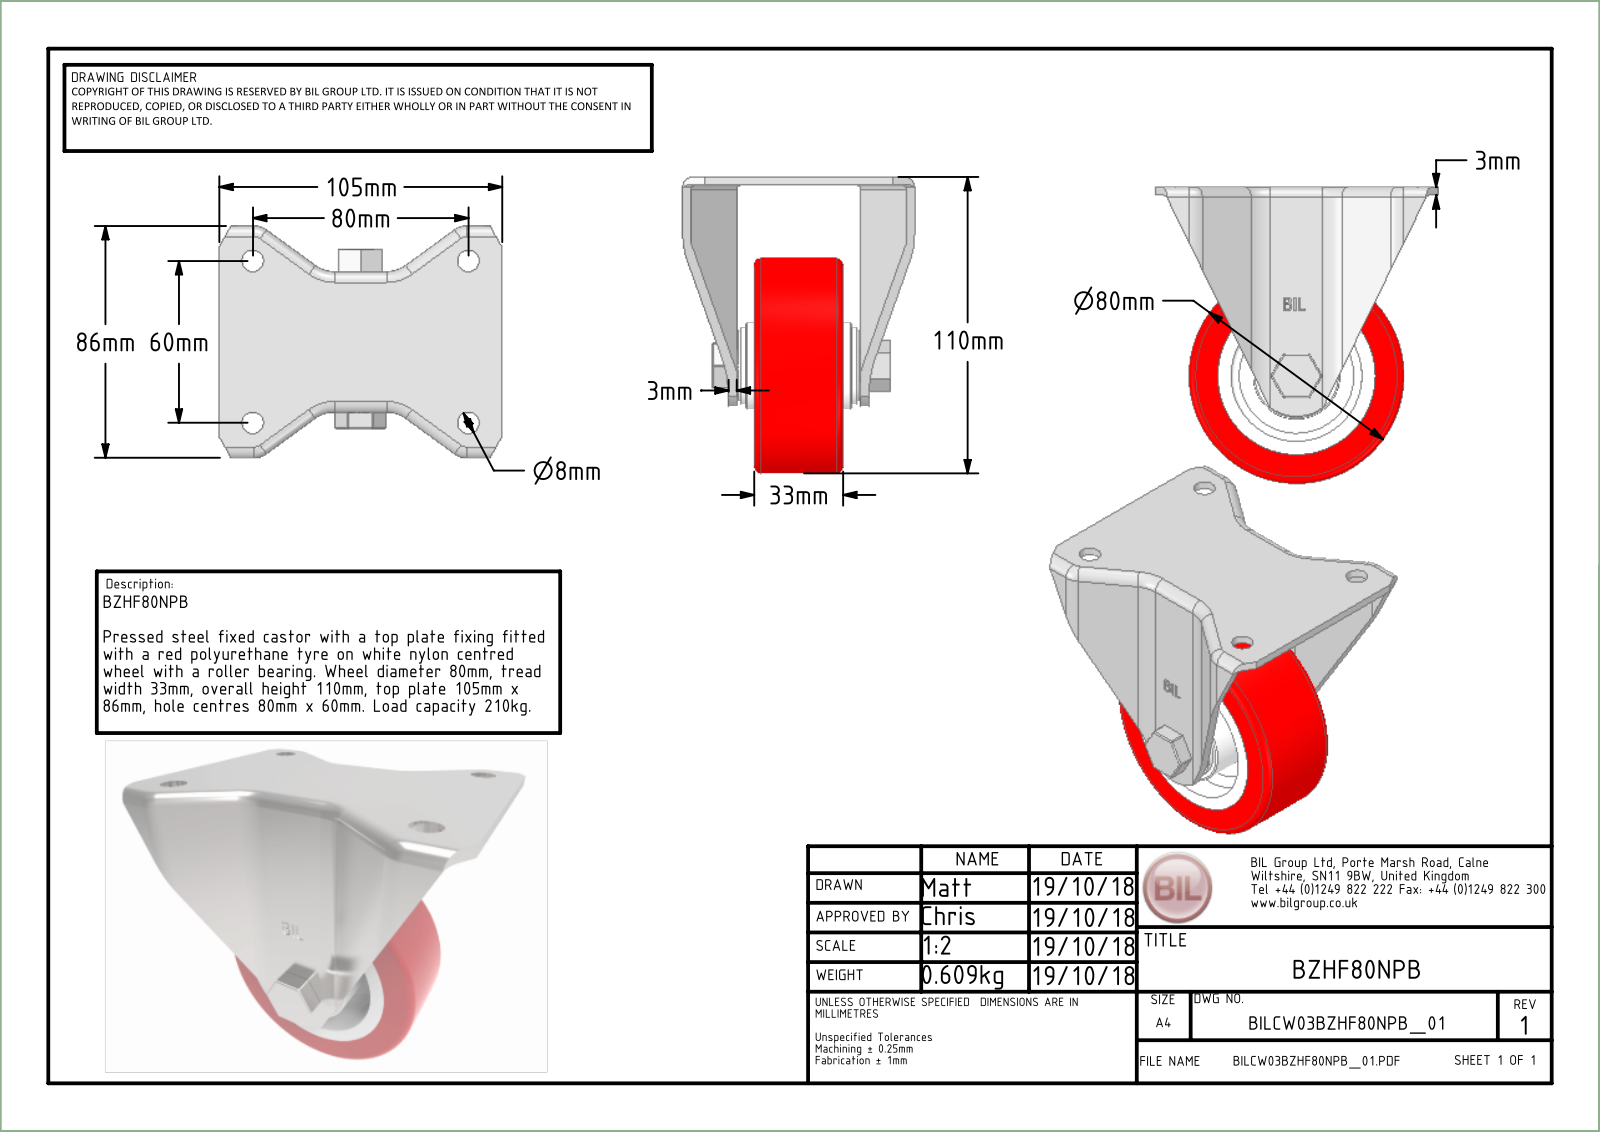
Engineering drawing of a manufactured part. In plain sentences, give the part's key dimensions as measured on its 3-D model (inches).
The part is named "BZHF80NPB v4; BZHF80AS v1; BZHF80AS; ZINC PLATED, PRESSED STEEL BRACKET (+8 more)". Its 3-D file was written by "Autodesk Translation Framework v14.10.0.0 (AUTOMOTIVE_DESIGN)". It is 17 solids with 485 faces: 220 planar, 163 cylindrical and 102 other. Overall it measures 4.331 by 4.134 by 3.425 inches. Its volume is 11.99 cubic inches and its surface area 141.4 square inches. Round holes: 1 of diameter 0.394, 1 of diameter 0.402, 1 of diameter 0.472, 1 of diameter 0.492, 1 of diameter 0.512, 1 of diameter 0.819, 1 of diameter 0.886, 1 of diameter 2.323. Round bosses or shafts: 8 of diameter 0.148, 1 of diameter 1.033, 1 of diameter 0.878, 1 of diameter 0.768, 1 of diameter 0.63, 1 of diameter 0.47, 1 of diameter 0.388, 1 of diameter 0.32. Partial cylindrical surfaces (rounded edges, fillets, slot ends): 18 of radius 0.02, 12 of radius 0.118, 10 of radius 0.059, 9 of radius 0.394, 8 of radius 0.177, 6 of radius 0.03, 4 of radius 0.276, 4 of radius 0.512. The main face-to-face distances are 0.118, 0.079, 1.752, 0.335, 2.008, 0.453, 2.087, 1.634, 1.673, 1.299.
